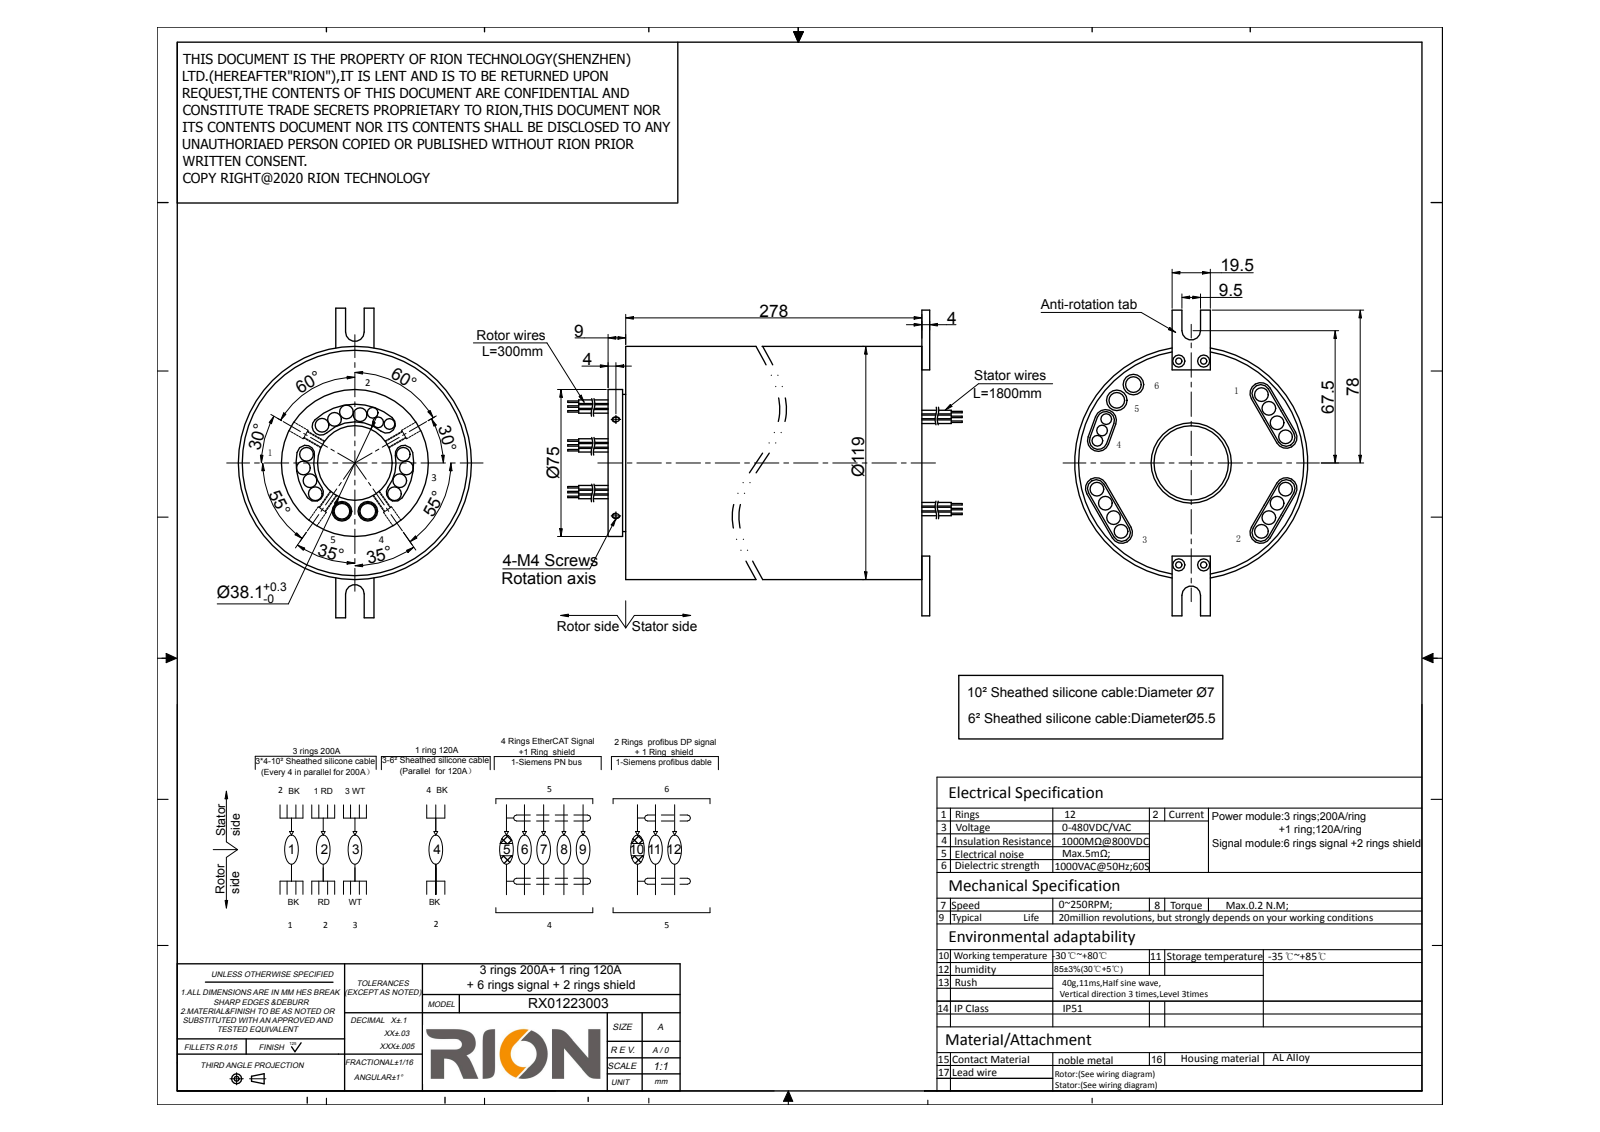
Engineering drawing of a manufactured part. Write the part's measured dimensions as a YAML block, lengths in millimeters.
part_name: "RX01223003"
step_written_by: "SolidWorks 2014 (CONFIG_CONTROL_DESIGN)"
units: millimeters
bodies: {solids: 1, faces: 233, planar: 86, cylindrical: 139, other: 8}
overall_size: [327, 156, 119]
volume: 2826000
surface_area: 188625
round_holes:
  - {diameter: 3.2, count: 4}
  - {diameter: 3.3, count: 4}
  - {diameter: 10, count: 2}
  - {diameter: 10.5, count: 2}
  - {diameter: 38.1, count: 1}
  - {diameter: 41.4, count: 1}
  - {diameter: 115.4, count: 1}
round_bosses_or_shafts:
  - {diameter: 7, count: 24}
  - {diameter: 5.5, count: 6}
  - {diameter: 8, count: 4}
  - {diameter: 119, count: 1}
  - {diameter: 115, count: 1}
  - {diameter: 75, count: 1}
  - {diameter: 70, count: 1}
  - {diameter: 41, count: 1}
partial_cylinders:
  - {radius: 4.5, count: 14}
  - {radius: 4.75, count: 2}
  - {radius: 21, count: 1}
  - {radius: 30, count: 1}
face_to_face_distances: [278, 9, 287, 20, 307, 291, 282, 4, 285, 276]
hole_center_spacings: [52.39, 12.7, 25.5, 27.37, 30.28, 76.63, 77.72, 104]
